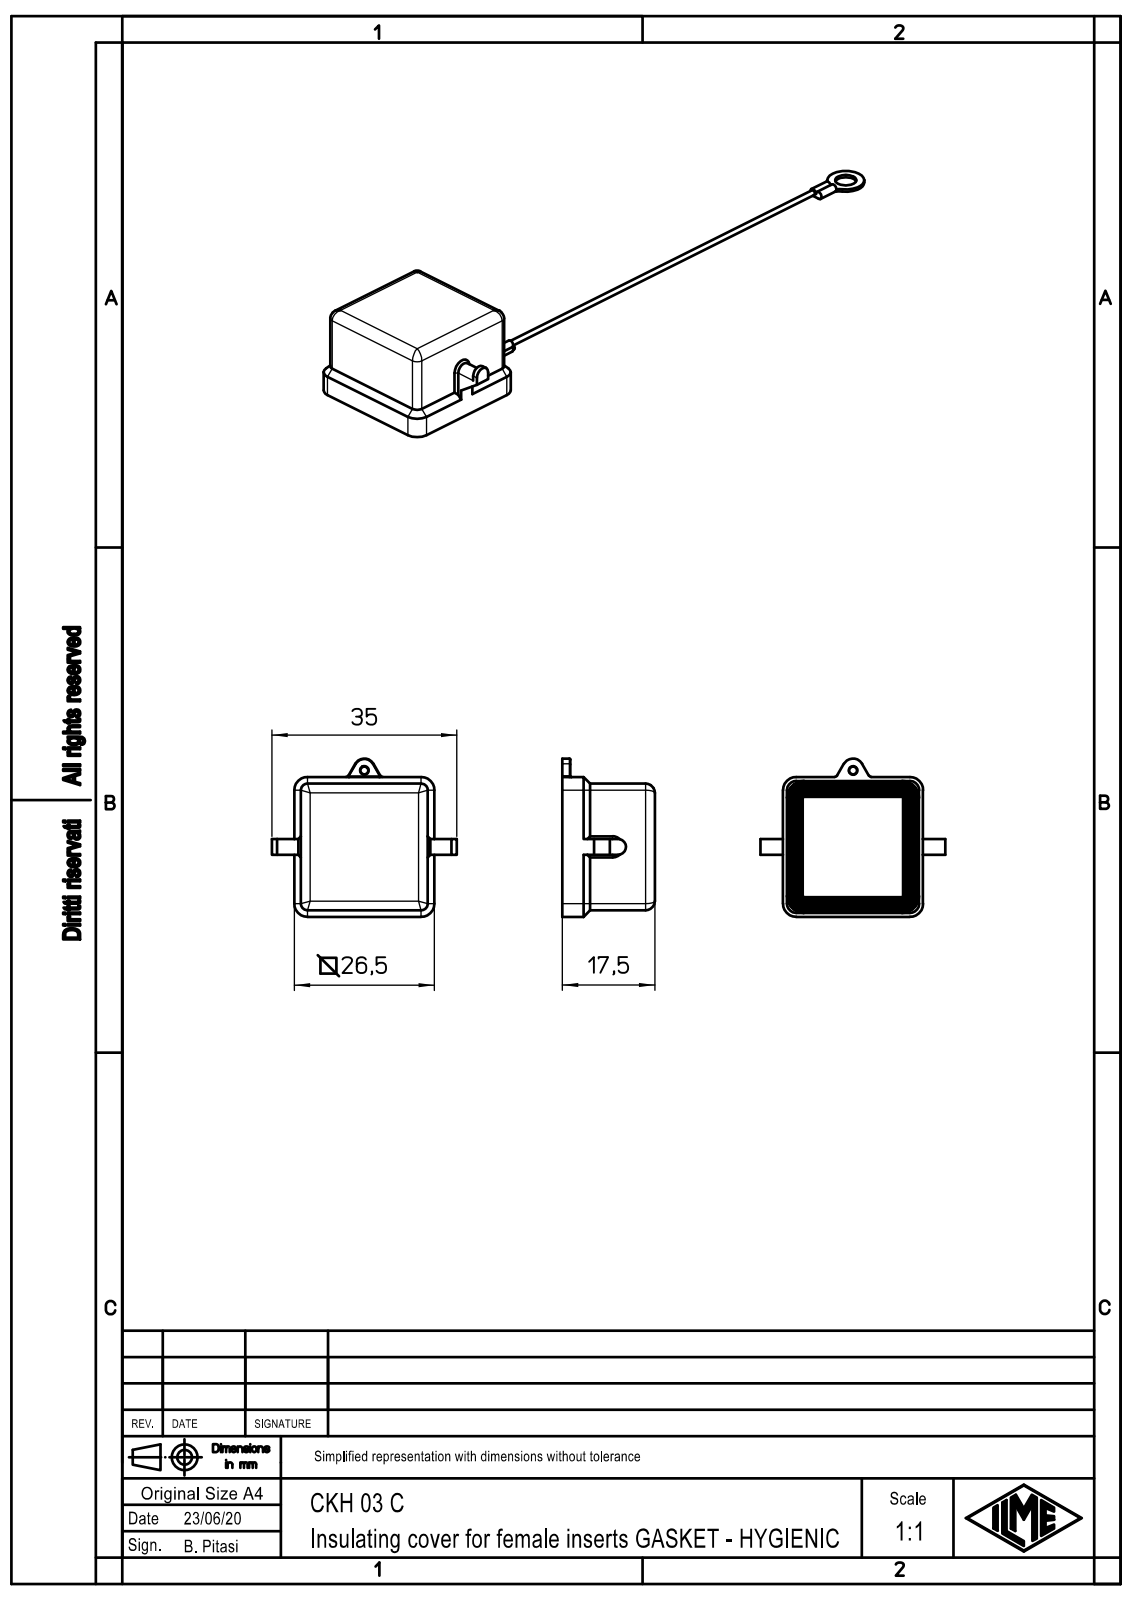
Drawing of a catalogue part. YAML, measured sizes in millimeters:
part_name: "CKH 03 C"
step_written_by: "Creo Elements/Direct Modeling 20.1B 02-Apr-2019 (C) Parametric Technology GmbH (AUTOMOTIVE_DESIGN)"
units: millimeters
bodies: {solids: 1, faces: 199, planar: 98, cylindrical: 75, other: 26}
overall_size: [130.75, 35, 20]
volume: 3847
surface_area: 5089
round_holes:
  - {diameter: 1.5, count: 1}
  - {diameter: 4, count: 1}
round_bosses_or_shafts:
  - {diameter: 1, count: 4}
  - {diameter: 7, count: 1}
partial_cylinders:
  - {radius: 0.25, count: 14}
  - {radius: 1.75, count: 12}
  - {radius: 0.2, count: 7}
  - {radius: 1.25, count: 4}
  - {radius: 2.5, count: 4}
  - {radius: 3.2, count: 4}
  - {radius: 0.5, count: 2}
  - {radius: 0.7, count: 2}
face_to_face_distances: [1.25, 22.75, 24, 21.5, 2.5, 2, 25.25, 14, 3.75, 20.25]
hole_center_spacings: [99.5]
